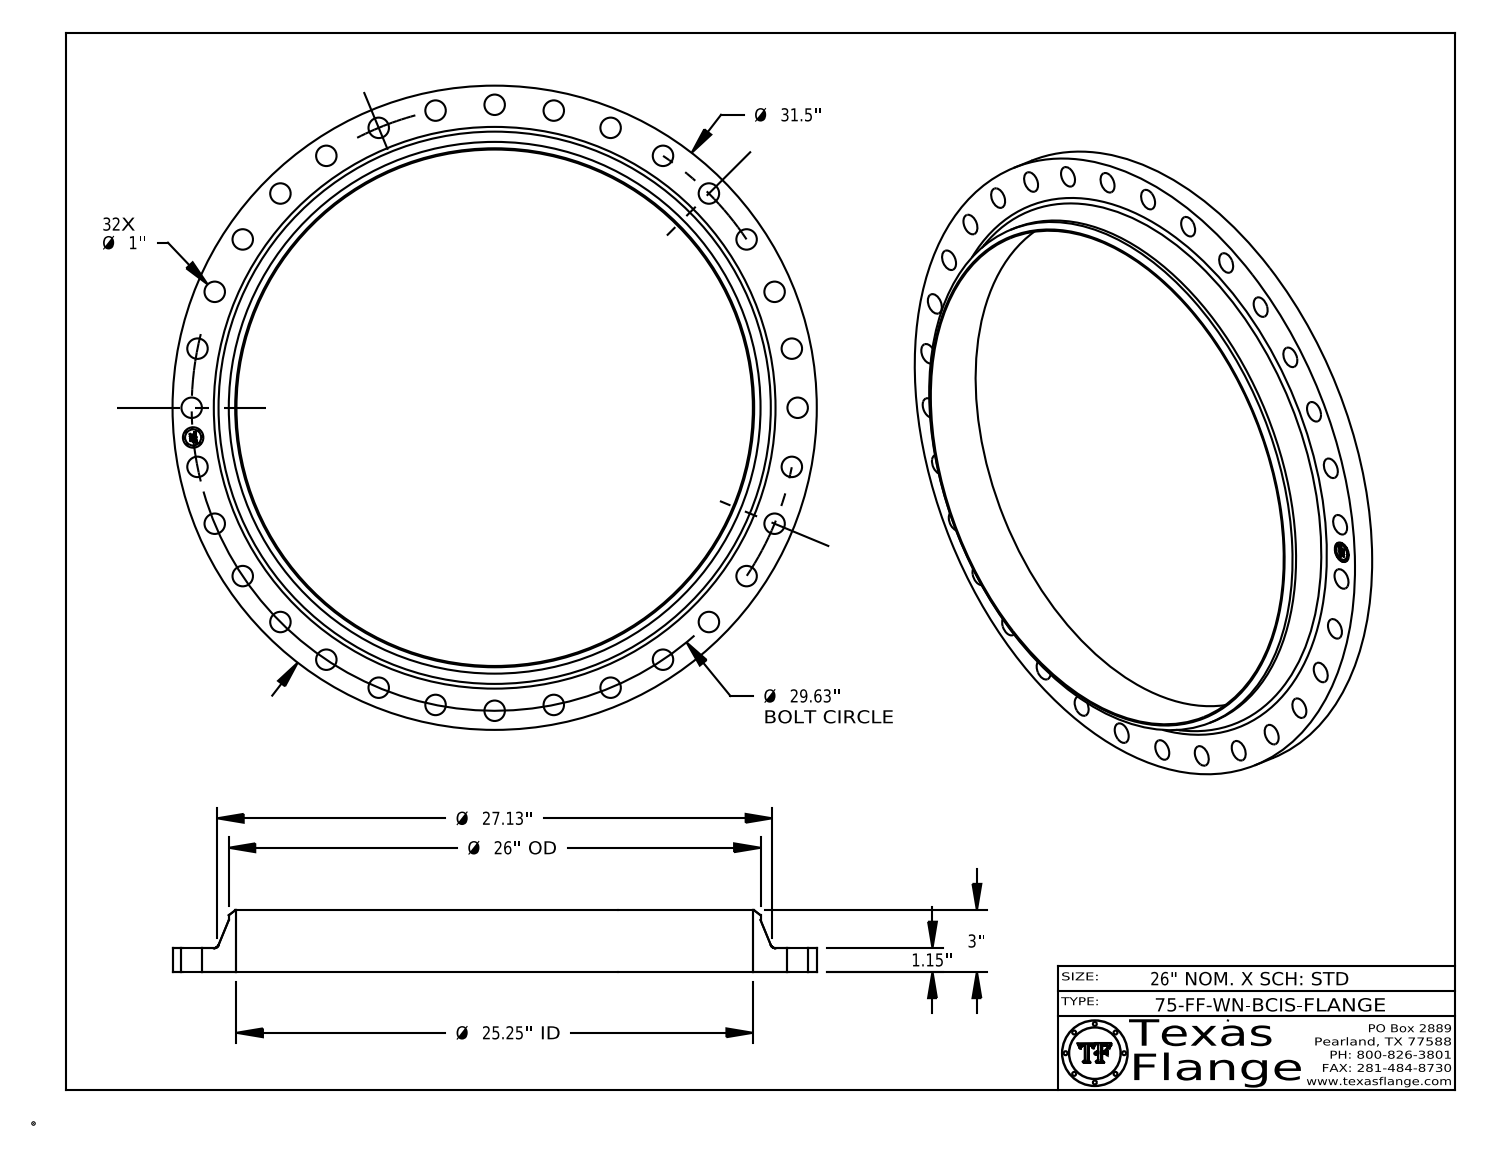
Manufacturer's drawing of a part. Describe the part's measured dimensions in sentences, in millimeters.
The part is named "75-FF-WN, BCIS". Its 3-D file was written by "CATIA V5 STEP AP214 (AUTOMOTIVE_DESIGN)". It is 1 solid with 464 faces: 368 planar, 90 cylindrical and 6 other. Overall it measures 800.1 by 800.1 by 76.2 millimeters. Its volume is 6 502 000 cubic millimeters and its surface area 700 600 square millimeters. Round holes: 33 of diameter 25.4, 1 of diameter 641.4. Round bosses or shafts: 8 of diameter 1.5, 1 of diameter 800.1, 1 of diameter 660.4, 1 of diameter 20. The main face-to-face distances are 31.8, 76.2, 44.5, 31.4, 0.4, 44.8, 7.6, 7.4, 1.4, 4.9. The hole center spacings are 73.8, 625.8, 376.3, 532.2, 695.3, 218.5, 354.8, 720.2.
